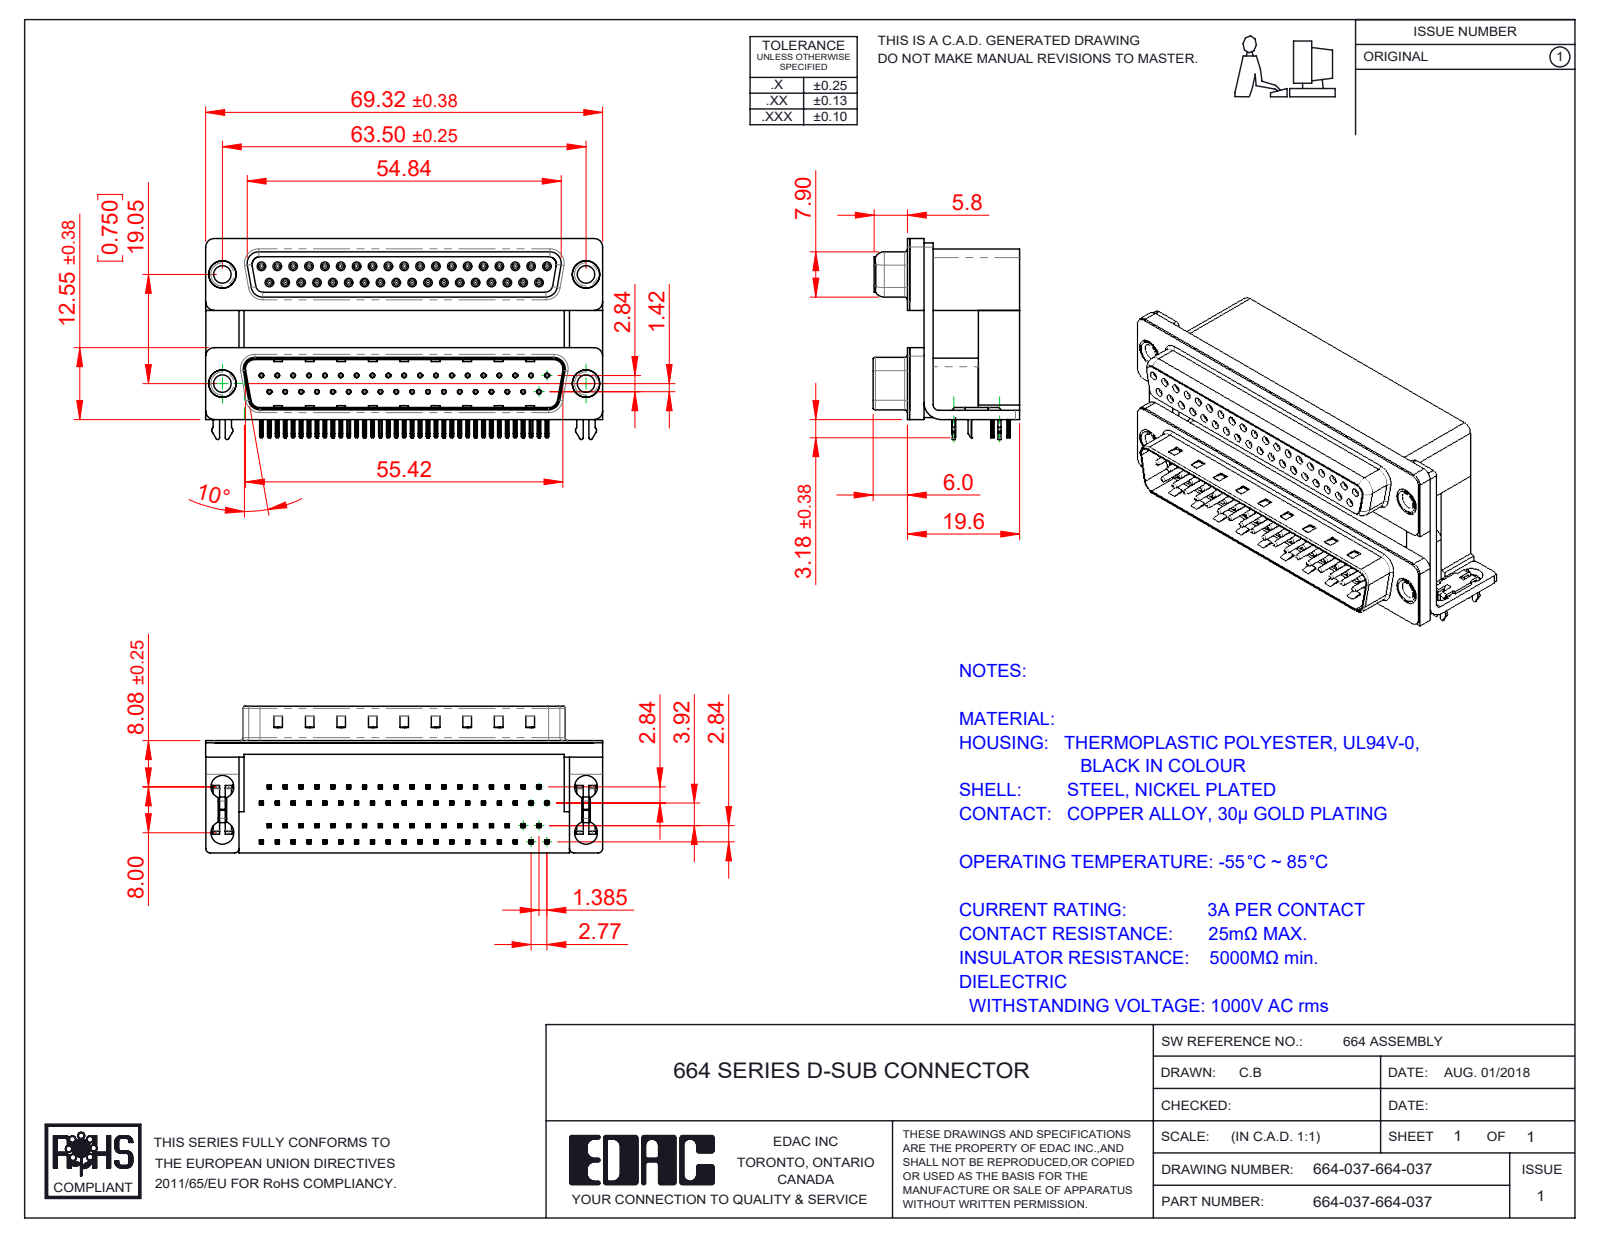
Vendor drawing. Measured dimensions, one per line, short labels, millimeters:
name: 664 Contact Bottom Upper_M; 664 Contact Top Upper_M; 664 Housing Spacer_37 Contacts M; 664 Contact Top Lower (+8 more)
written by: SolidWorks 2020 (CONFIG_CONTROL_DESIGN)
unit: mm
bodies: 87 solids, 9013 faces (4843 planar, 2191 cylindrical, 1979 other)
size: 69.32 × 35.1 × 25.6
volume: 31 087 mm³; area: 32 846 mm²
holes: 74× ⌀0.8, 37× ⌀0.35, 37× ⌀0.9, 8× ⌀4, 4× ⌀3.05, 4× ⌀3.5, 4× ⌀4.8, 4× ⌀5
bosses: 37× ⌀1.2, 37× ⌀0.75, 4× ⌀4.9, 4× ⌀4.75, 4× ⌀3.85
rounds: 298× R0.1, 158× R0.25, 148× R0.15, 74× R0.12, 74× R0.35, 37× R0.34, 18× R0.28, 16× R0.5
face distances: 0.4, 19.2, 7.2, 12, 10.69, 2.19, 2.84, 18.7, 29.39, 19.05
hole spacings: 2.77, 5.54, 3.16, 8.31, 11.08, 13.85, 16.62, 19.39
